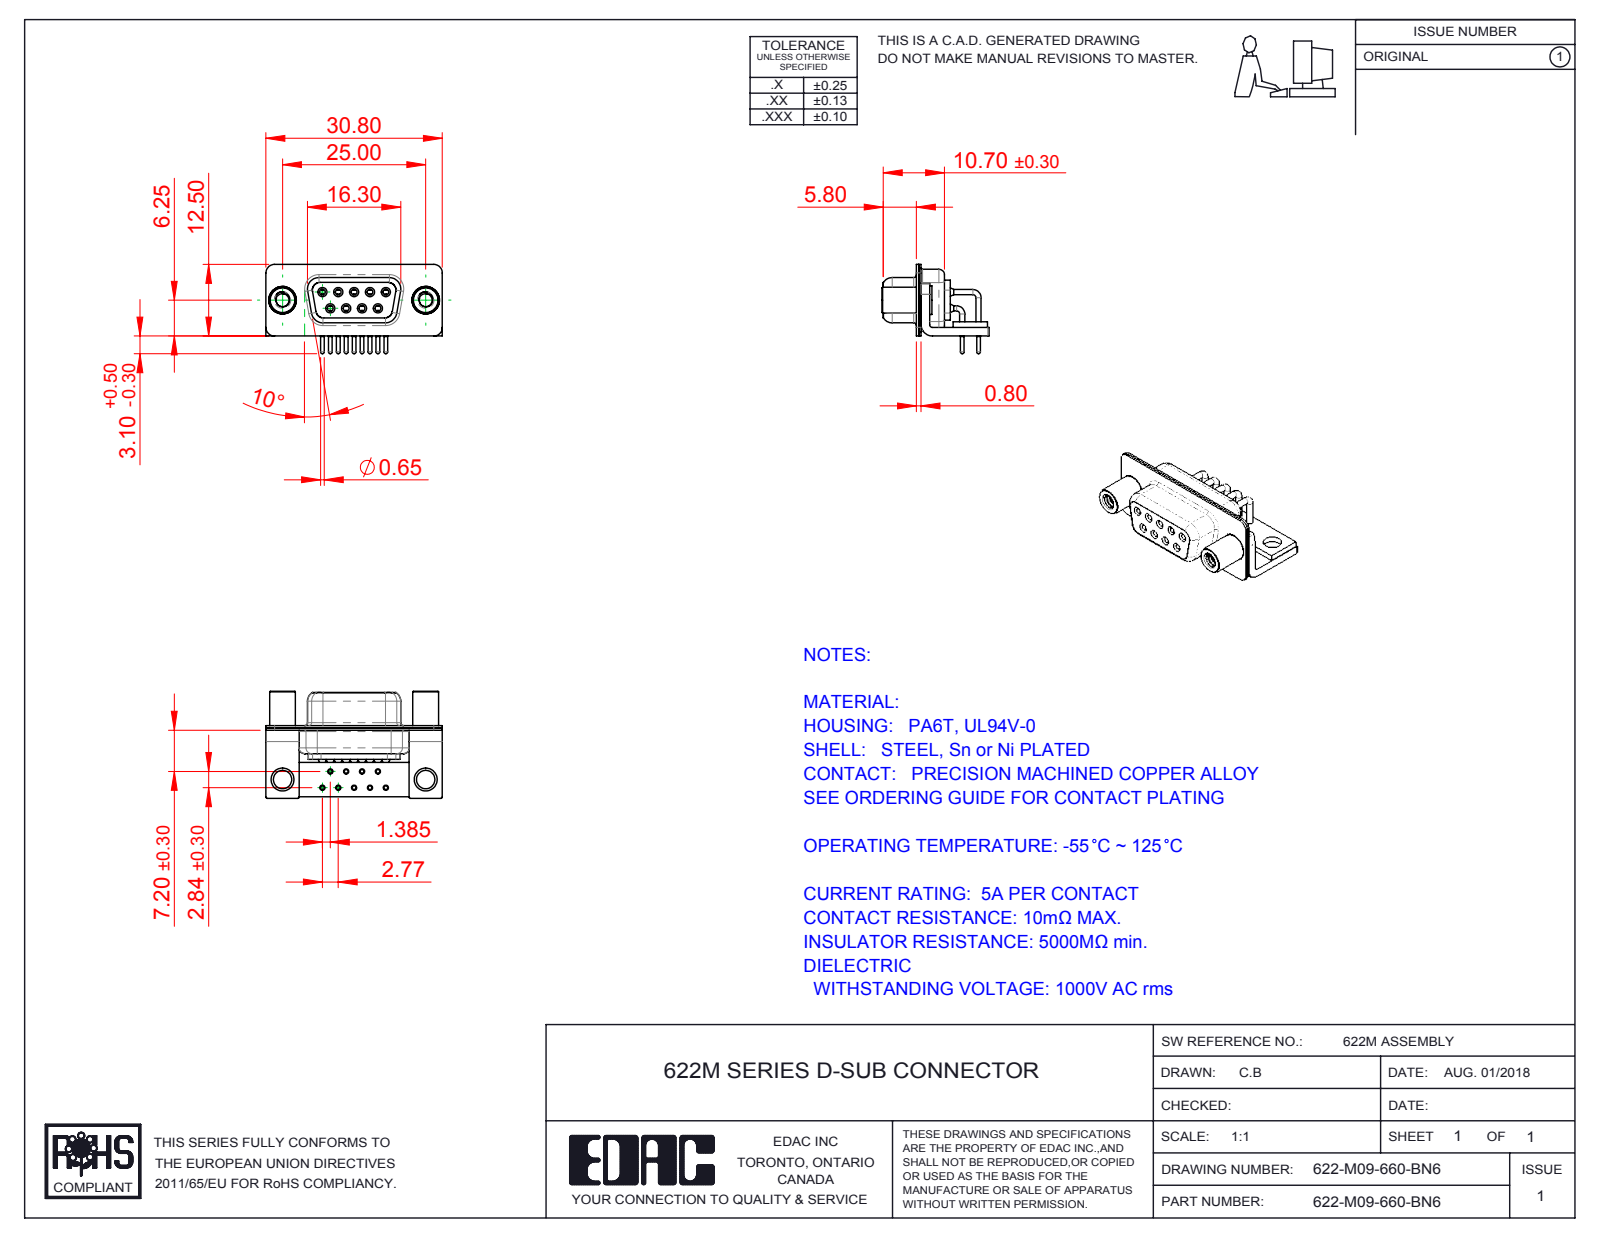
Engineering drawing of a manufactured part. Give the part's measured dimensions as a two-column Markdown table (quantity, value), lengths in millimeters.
| quantity | value |
| --- | --- |
| part name | 622M 4-40 Threaded Standoff; 622M Stabilizer Bracket; 622M Contact Row 2; 622M Contact Row 1 (+5 more) |
| STEP written by | SolidWorks 2016 (CONFIG_CONTROL_DESIGN) |
| units | millimeters |
| bodies | 17 solids, 874 faces (230 planar, 426 cylindrical, 218 other) |
| overall size | 30.8 × 18.7 × 15.6 |
| volume | 2 258 mm³ |
| surface area | 5 841 mm² |
| round holes (diameter × count) | 0.9 × 9, 1 × 9, 1.1 × 9, 1.7 × 9, 1.8 × 9, 2 × 9, 2.26 × 2, 3.2 × 2, 4 × 2, 4.8 × 2 |
| round bosses / shafts (diameter × count) | 1.6 × 9, 1.5 × 9, 0.9 × 9, 0.65 × 9, 5 × 2, 4.9 × 2, 4.5 × 2 |
| partial cylindrical surfaces (radius × count) | 0.25 × 16, 1.5 × 16, 2 × 13, 1.35 × 8, 1.6 × 8, 0.5 × 5, 0.6 × 4, 0.65 × 4 |
| main face-to-face distances | 0.4, 0.8, 2.3, 1.9, 1.5, 1, 9.35, 1.45, 8.5, 8.95 |
| hole center spacings | 3.16, 2.77, 5.54, 5.03, 5.04, 8.31, 7.48, 7.49 |
